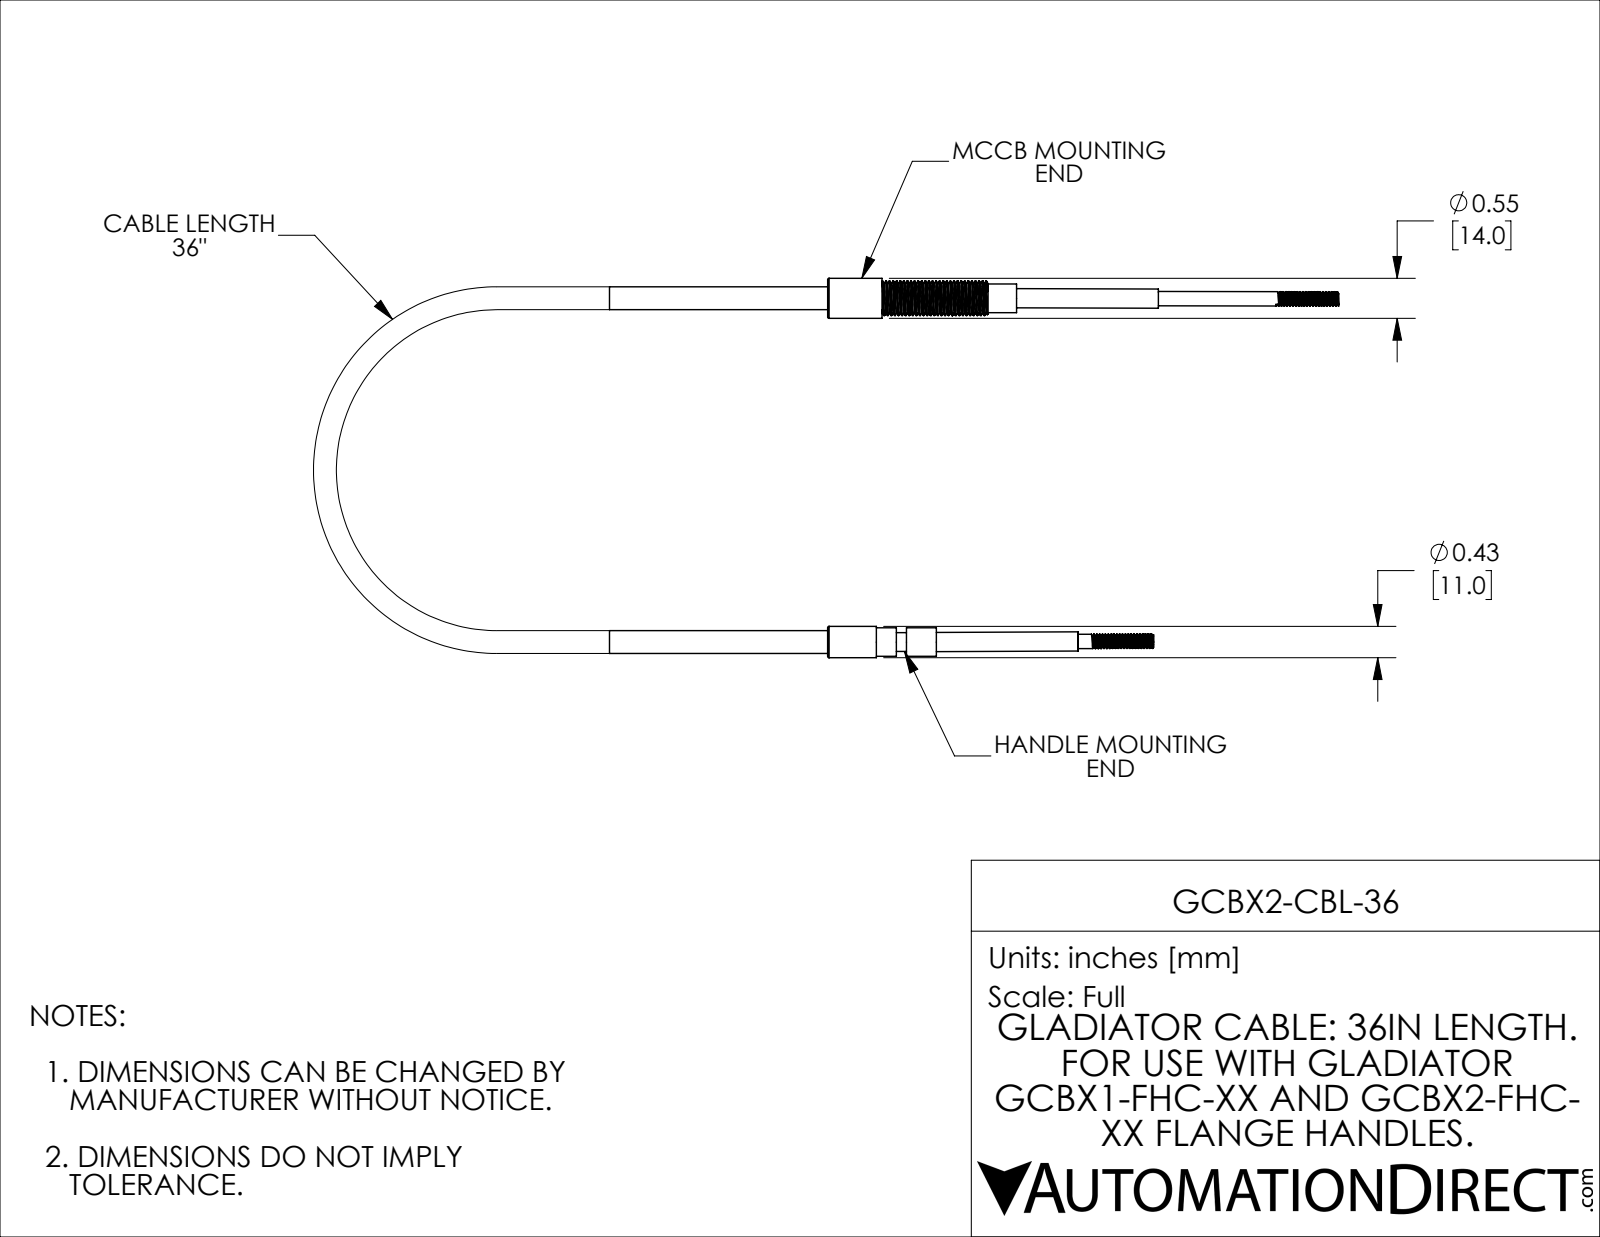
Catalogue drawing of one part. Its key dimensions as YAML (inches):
part_name: "GCBX2-CBL-36_2; GCBX2-CBL-36_1; GCBX2-CBL-36"
step_written_by: "SolidWorks 2021 (CONFIG_CONTROL_DESIGN)"
units: inches
bodies: {solids: 8, faces: 273, planar: 30, cylindrical: 187, other: 56}
overall_size: [10.028, 5.217, 1.358]
volume: 1.36
surface_area: 29.56
round_holes:
  - {diameter: 0.201, count: 2}
  - {diameter: 0.118, count: 1}
  - {diameter: 0.245, count: 1}
  - {diameter: 0.256, count: 1}
  - {diameter: 0.315, count: 1}
round_bosses_or_shafts:
  - {diameter: 0.394, count: 2}
  - {diameter: 0.287, count: 2}
  - {diameter: 0.264, count: 2}
  - {diameter: 0.197, count: 2}
  - {diameter: 0.551, count: 1}
  - {diameter: 0.472, count: 1}
  - {diameter: 0.433, count: 1}
  - {diameter: 0.315, count: 1}
face_to_face_distances: [1.181, 3, 1.819, 2.598, 3.78, 5.598, 0.748, 1.85, 1.929, 0.413]
hole_center_spacings: [4.803]
